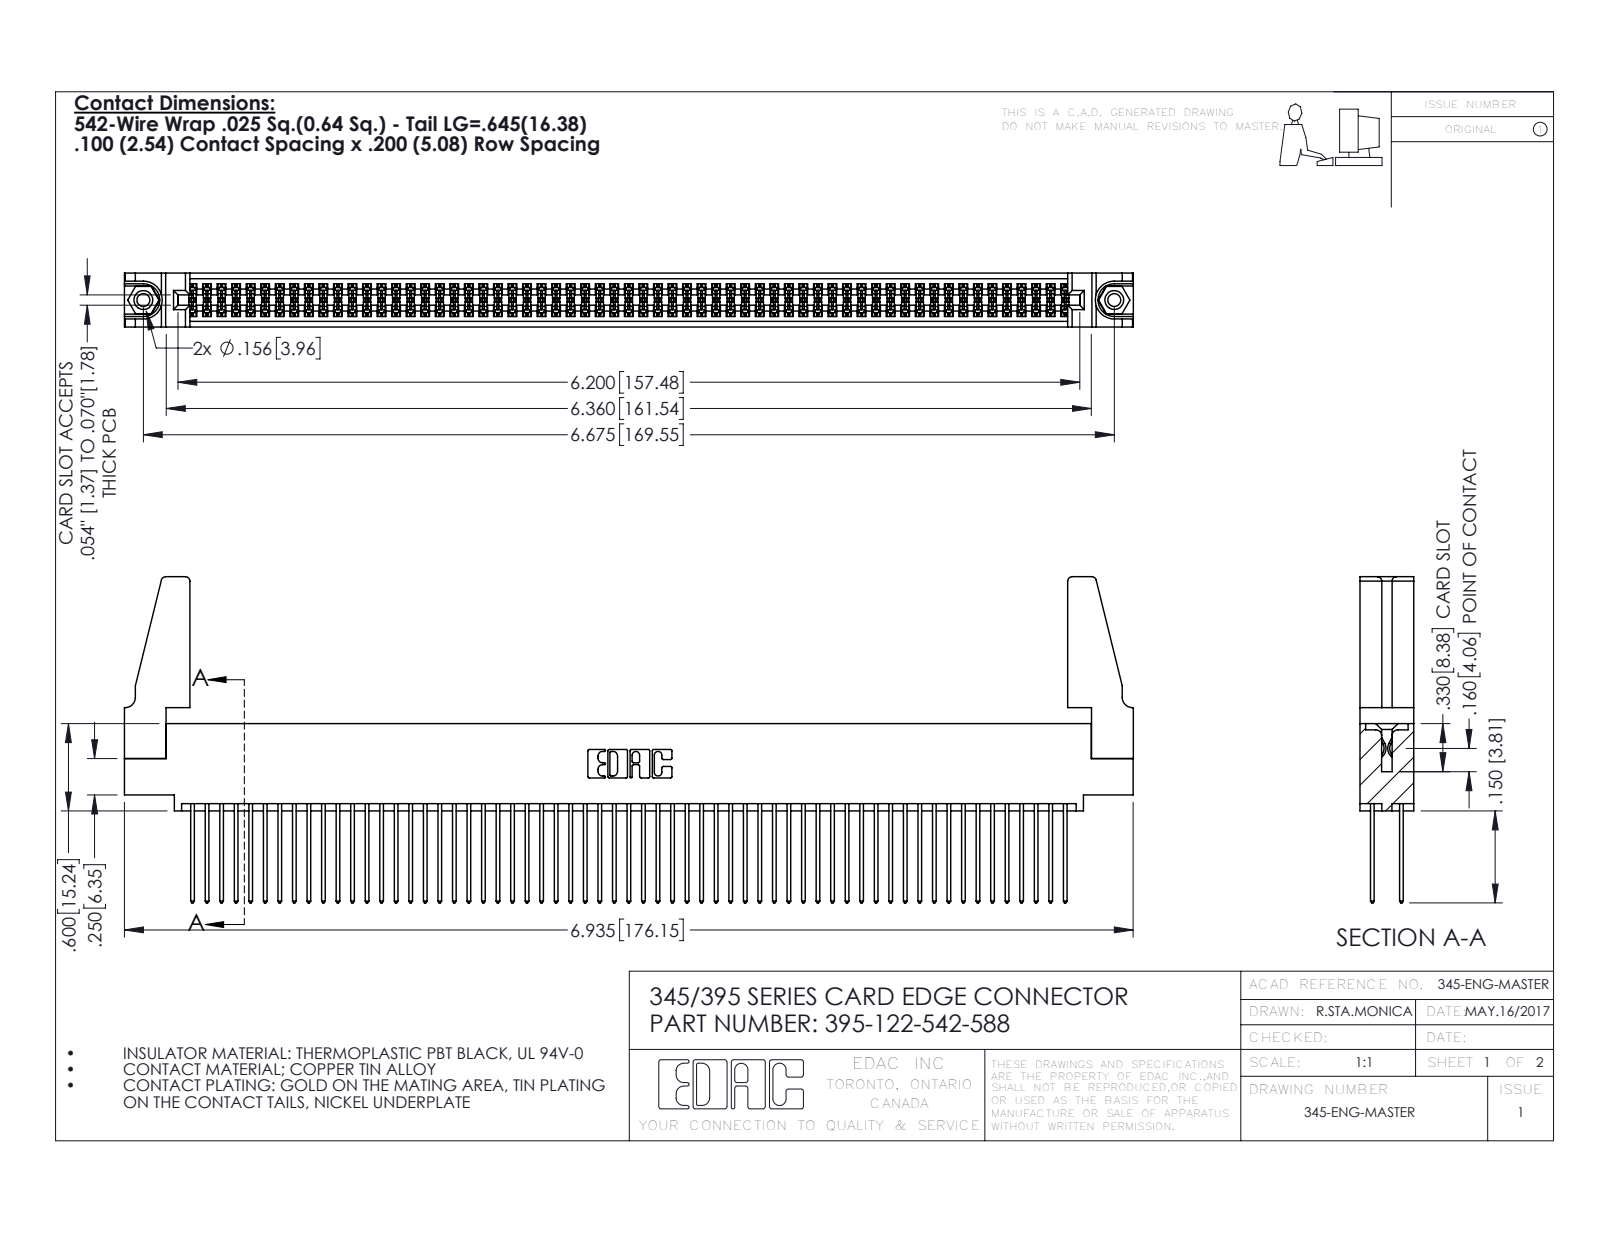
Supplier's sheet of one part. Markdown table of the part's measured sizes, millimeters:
| quantity | value |
| --- | --- |
| part name | 345-292-001_345-293-142; 345-220-078_345-220-088; 395-122-542-588; 345 Part_0.110 Offset - 0.156 Dia-TH (+1 more) |
| STEP written by | SolidWorks 2016 (CONFIG_CONTROL_DESIGN) |
| units | millimeters |
| bodies | 127 solids, 6354 faces (4182 planar, 2156 cylindrical, 16 other) |
| overall size | 176.2 × 56.9 × 9.4 |
| volume | 21 040 mm³ |
| surface area | 32 530 mm² |
| round holes (diameter × count) | 2.3 × 2, 3.2 × 2, 4 × 2, 1.6 × 1 |
| round bosses / shafts (diameter × count) | 3.9 × 2 |
| partial cylindrical surfaces (radius × count) | 0.2 × 183, 0.3 × 122, 0.3 × 22, 0.8 × 8, 0.2 × 6, 0.8 × 6, 0.7 × 3, 0.4 × 2 |
| main face-to-face distances | 1.8, 7.6, 5.1, 2.5, 6.9, 0.6, 9.4, 5.7, 4.4, 3.8 |
| hole center spacings | 6.9, 163.6, 169.5 |
